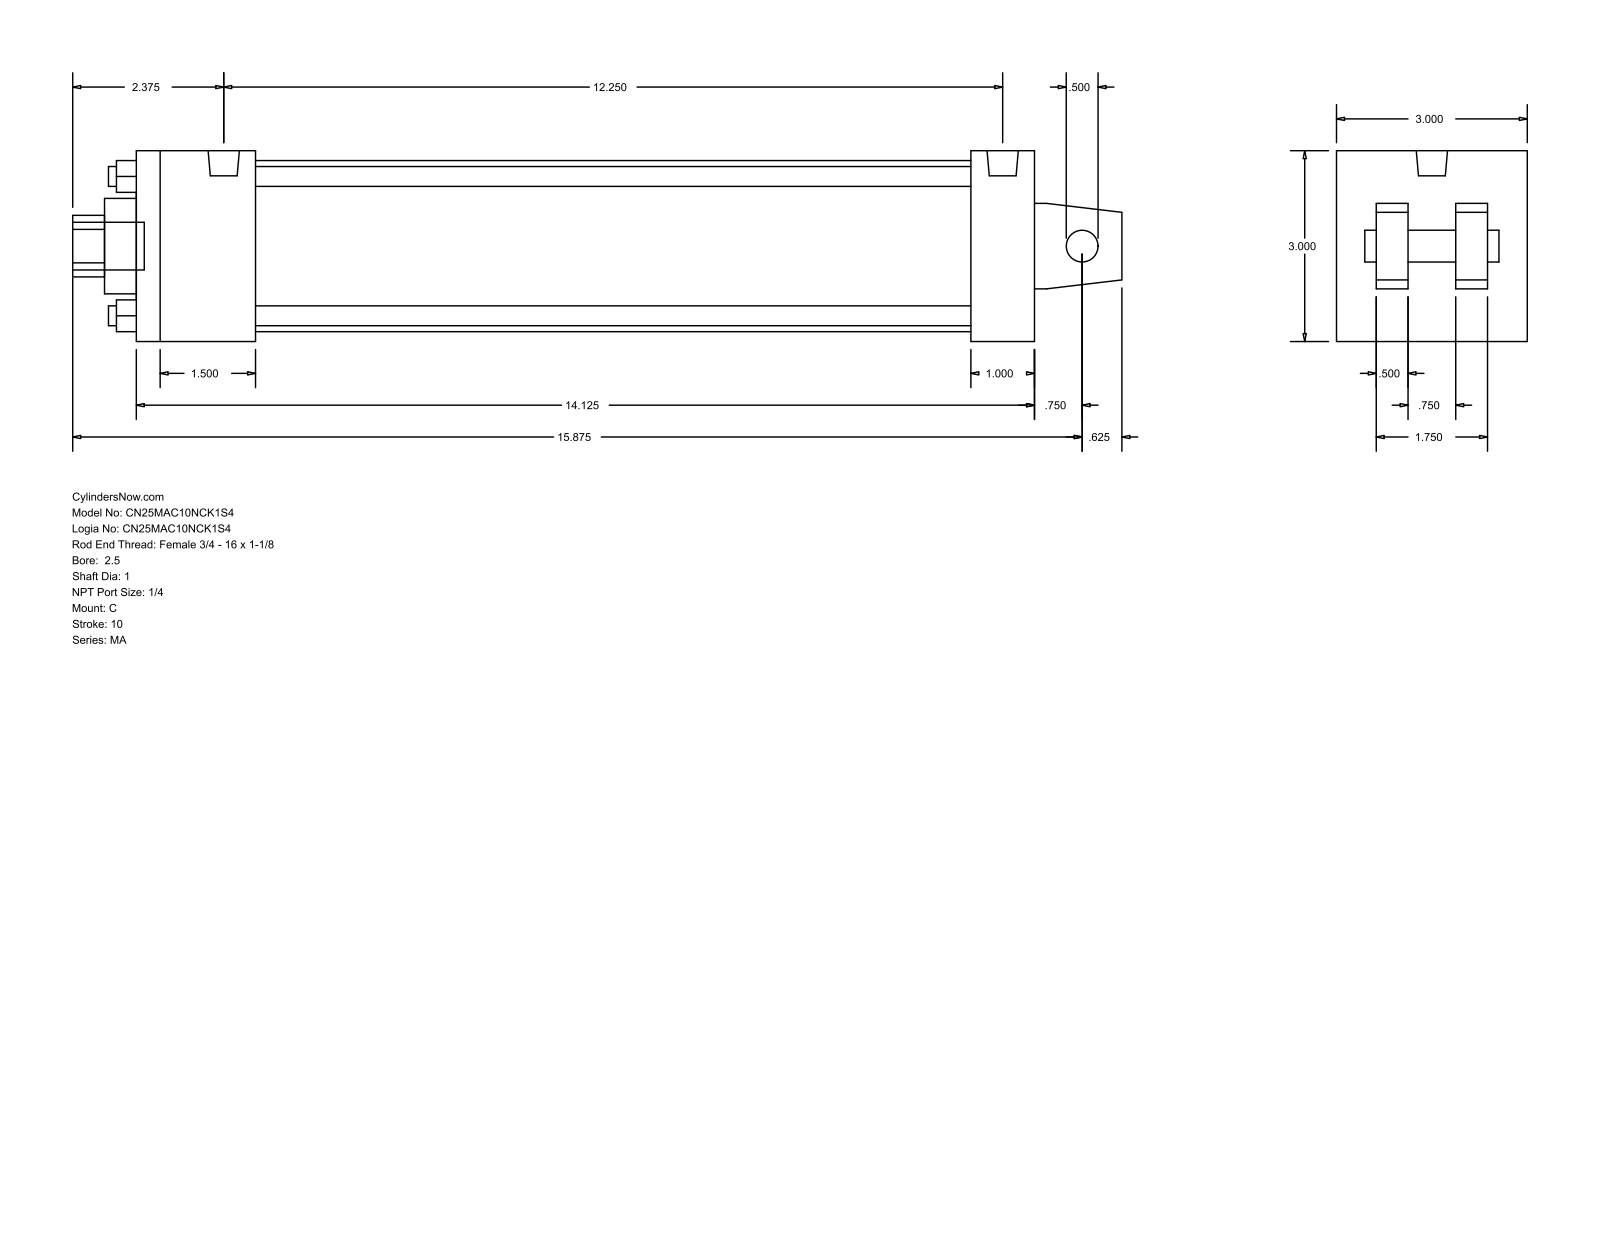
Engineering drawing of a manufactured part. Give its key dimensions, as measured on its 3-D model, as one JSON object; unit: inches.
{"part_name": "MA_C__0250_1", "step_written_by": "GSSL Pune (CONFIG_CONTROL_DESIGN)", "units": "inches", "bodies": {"solids": 0, "faces": 103, "planar": 76, "cylindrical": 27, "other": 0}, "overall_size": [16.5, 3, 3], "round_holes": [[0.313, 4], [0.5, 1], [1, 1], [1.5, 1], [2.69, 1]], "round_bosses_or_shafts": [[0.313, 4], [0.492, 2], [0.75, 1]], "partial_cylinders_radius": [[0.484, 1]], "face_to_face_distances": [3, 1.875, 14.125, 0.5, 2.375, 0.625, 1.125, 13.125, 11.25, 12.25], "hole_center_spacings": [1.548, 2.19, 3.097]}
